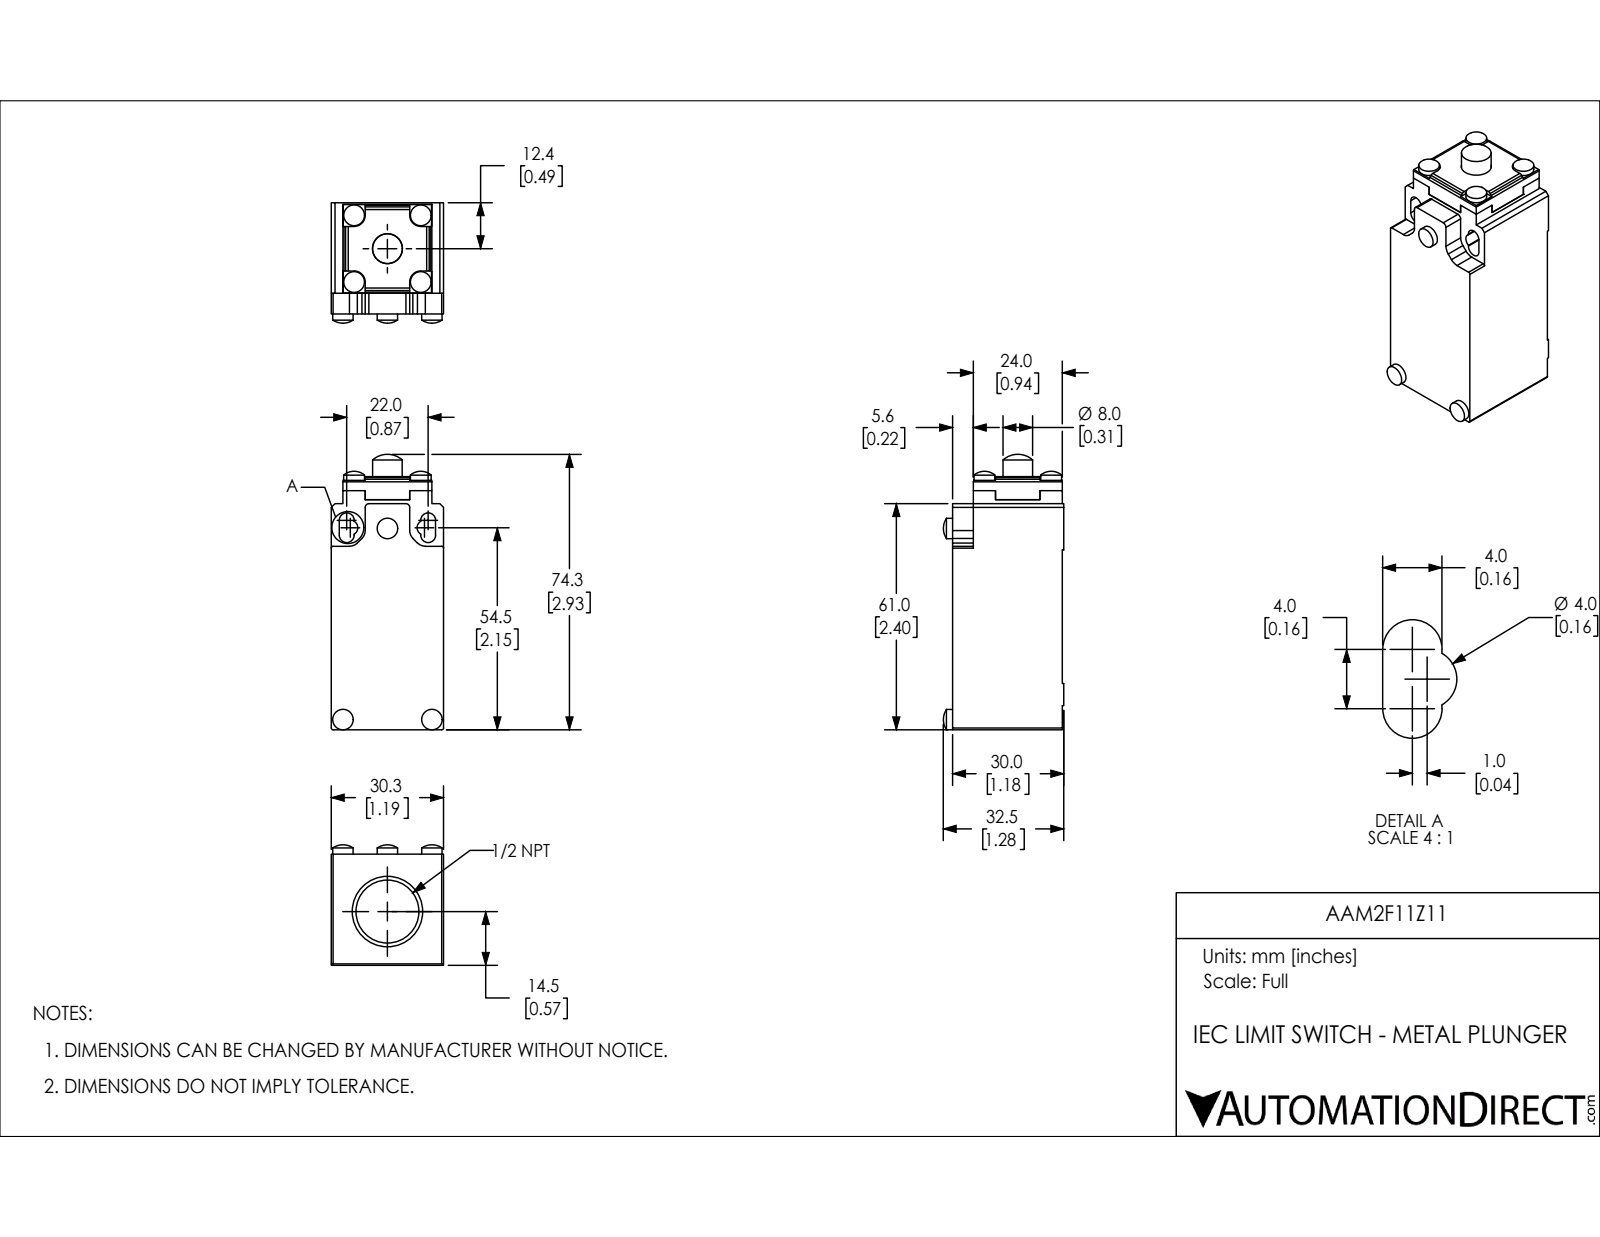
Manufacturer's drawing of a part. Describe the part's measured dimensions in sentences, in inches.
The part is named "AAM2F11Z11". Its 3-D file was written by "SolidWorks 2018 (AUTOMOTIVE_DESIGN)". It is 3 solids with 173 faces: 80 planar, 78 cylindrical and 15 other. Overall it measures 2.925 by 1.28 by 1.193 inches. Its volume is 3.382 cubic inches and its surface area 20.06 square inches. Round holes: 1 of diameter 0.319, 1 of diameter 0.669, 1 of diameter 0.748. Round bosses or shafts: 4 of diameter 0.22, 3 of diameter 0.217, 1 of diameter 0.315. Partial cylindrical surfaces (rounded edges, fillets, slot ends): 10 of radius 0.039, 8 of radius 0.118, 6 of radius 0.079, 4 of radius 0.02, 1 of radius 0.394, 1 of radius 0.4. The main face-to-face distances are 1.193, 1.165, 0.016, 1.181, 0.236, 2.444, 0.945, 2.445, 2.689, 0.245. The hole center spacings are 0.083.
